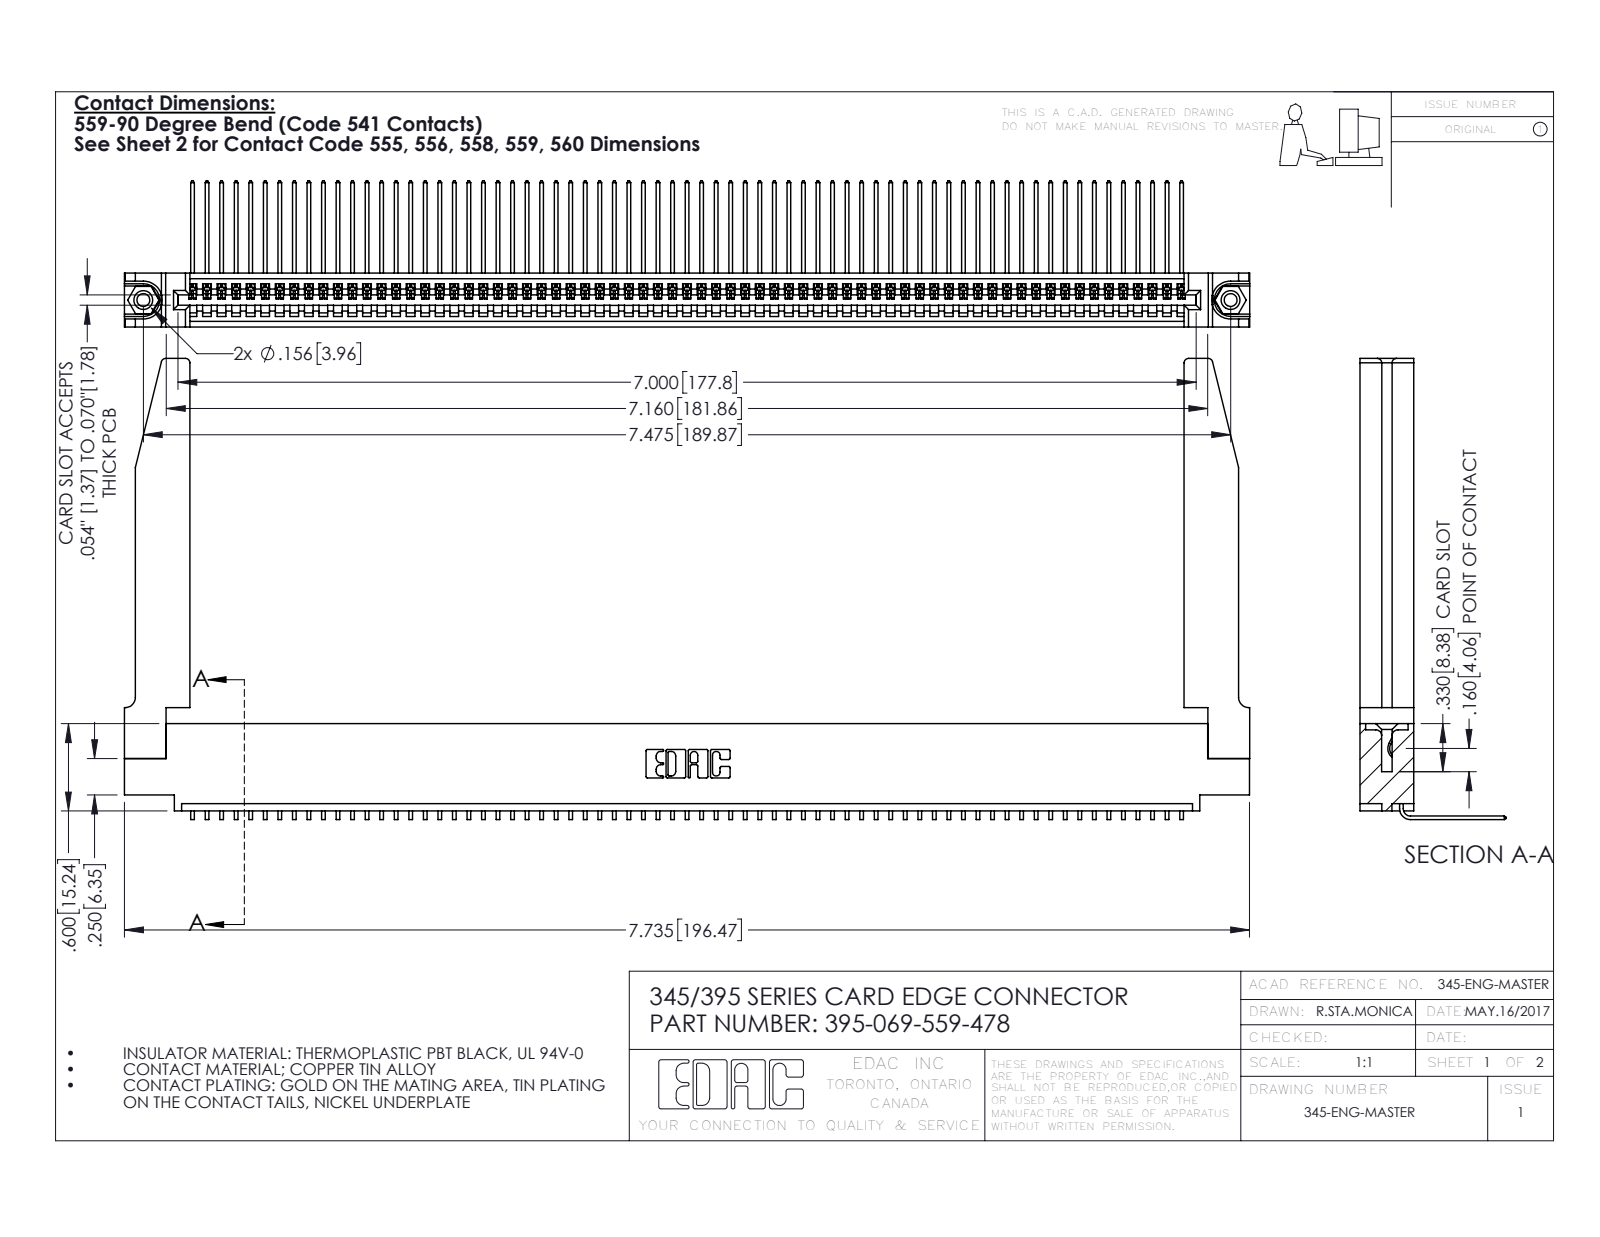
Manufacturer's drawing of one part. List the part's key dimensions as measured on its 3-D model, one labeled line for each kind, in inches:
Part name (STEP PRODUCT): 345-220-078_345-220-078; 345-292-001_558 559 Tail - 1; 345 Part_0.110 Offset - 0.156 Dia-TH; 345-250-001_345-250-001-102 (+1 more)
STEP written by: SolidWorks 2016 (CONFIG_CONTROL_DESIGN)
Units: inches
Bodies: 74 solids, 4504 faces (3124 planar, 1328 cylindrical, 52 other)
Overall size (bounding box): 7.736 × 3.169 × 1.005
Volume: 1.636 in³ · Surface area: 52.62 in²
Round holes (diameter × count): ⌀0.089 ×2, ⌀0.125 ×2, ⌀0.156 ×2, ⌀0.064 ×1
Round bosses / shafts (diameter × count): ⌀0.155 ×2
Partial cylindrical surfaces — rounded edges, fillets, slot ends (radius × count): R0.006 ×138, R0.01 ×22, R0.03 ×8, R0.007 ×6, R0.031 ×6, R0.026 ×3, R0.031 ×2, R0.04 ×2
Main face-to-face distances: 0.072, 0.37, 0.298, 0.098, 0.272, 0.025, 0.2, 0.225, 0.149, 0.148
Hole centre spacings: 0.27, 7.239, 7.475
